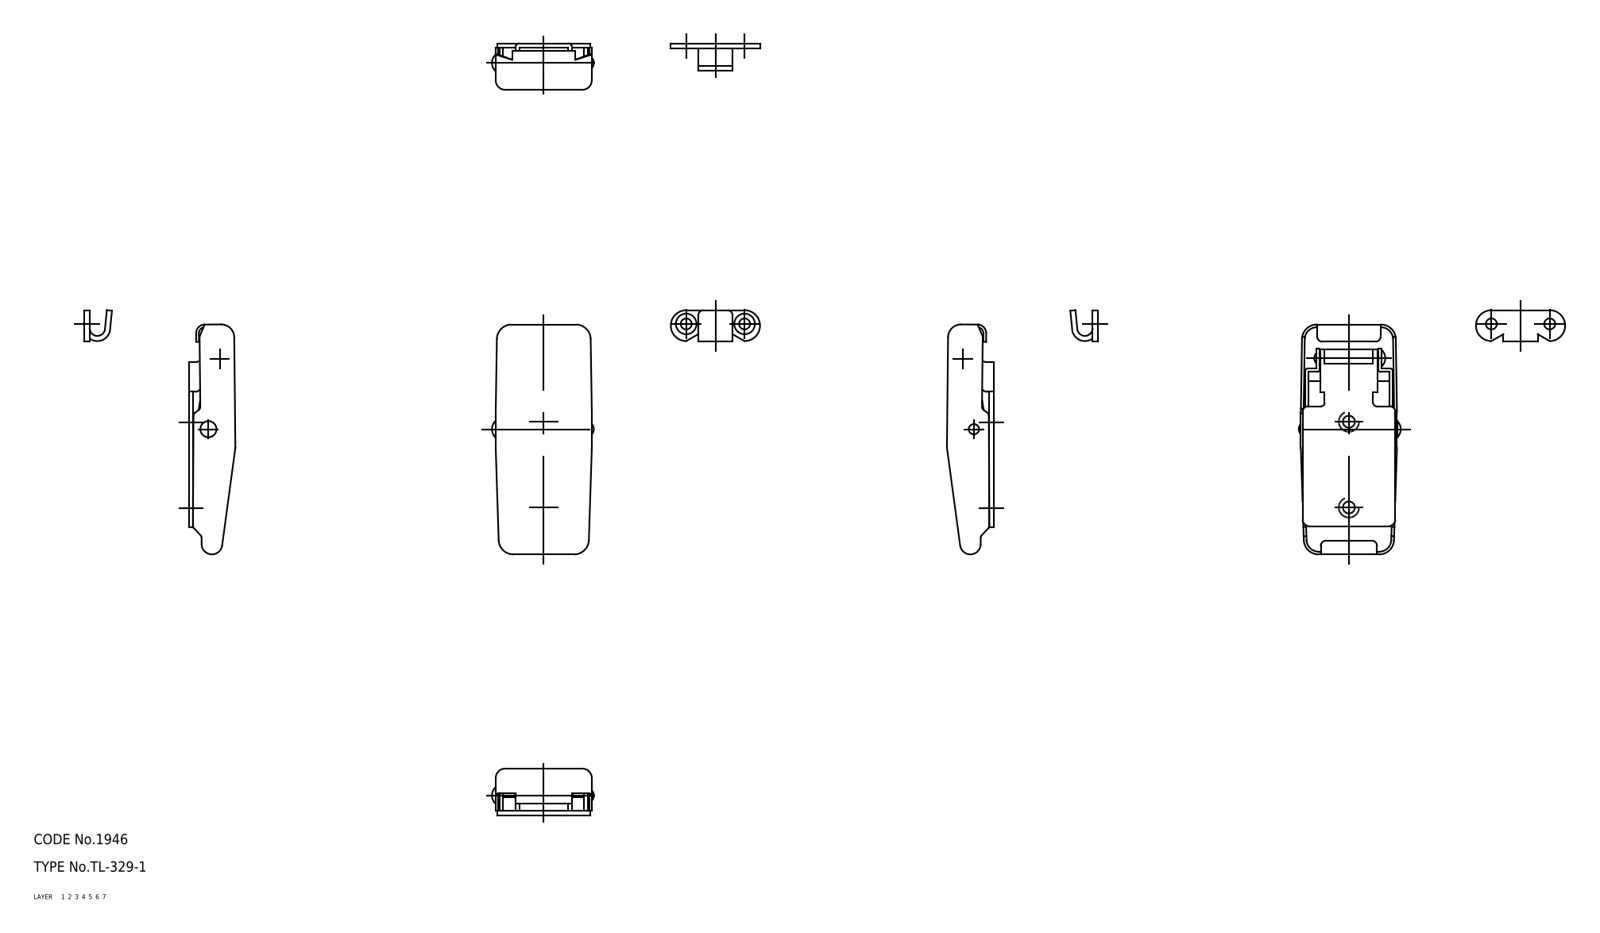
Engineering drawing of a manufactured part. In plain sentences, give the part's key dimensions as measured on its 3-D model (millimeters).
The part is named "67122601; 67122614; 67122627; 67122640 (+2 more)". Its 3-D file was written by "CADfix (AUTOMOTIVE_DESIGN)". It is 6 solids with 261 faces: 0 planar, 0 cylindrical and 261 other. Overall it measures 66.99 by 29.7 by 13.57 millimeters. Its volume is 5 522 cubic millimeters and its surface area 12 411 square millimeters.
